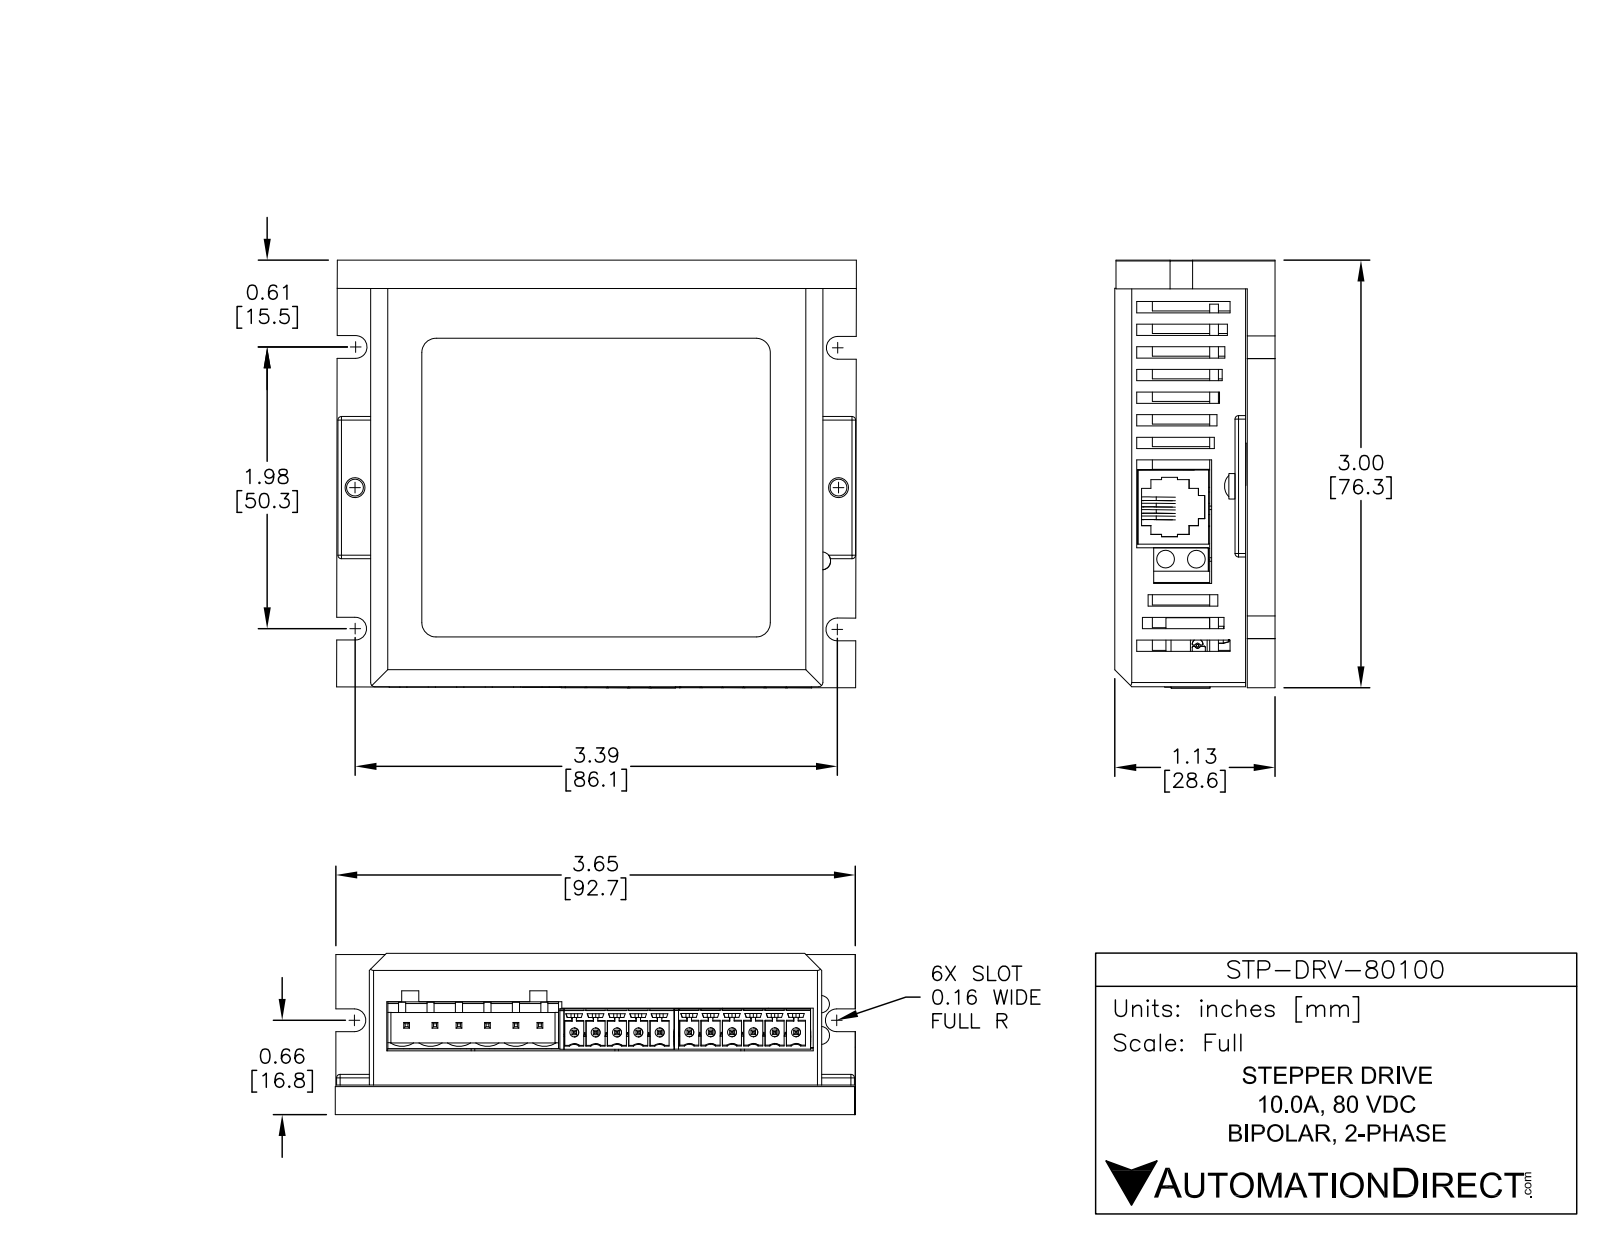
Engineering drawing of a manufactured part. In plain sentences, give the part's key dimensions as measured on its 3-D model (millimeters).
The part is named "STP-DRV-80100". Its 3-D file was written by "SolidWorks 2014 (AUTOMOTIVE_DESIGN)". It is 1 solid with 235 faces: 178 planar, 51 cylindrical and 6 other. Overall it measures 92.7 by 76.3 by 28.6 millimeters. Its volume is 60 530 cubic millimeters and its surface area 39 260 square millimeters. Round holes: 2 of diameter 3.6. Partial cylindrical surfaces (rounded edges, fillets, slot ends): 8 of radius 0.6, 7 of radius 0.8, 6 of radius 2, 4 of radius 2.5. The main face-to-face distances are 5, 21.6, 26.6, 1.5, 28.1, 23.1, 1.9, 0.4, 28.5, 23.5. The hole center spacings are 86.4.
